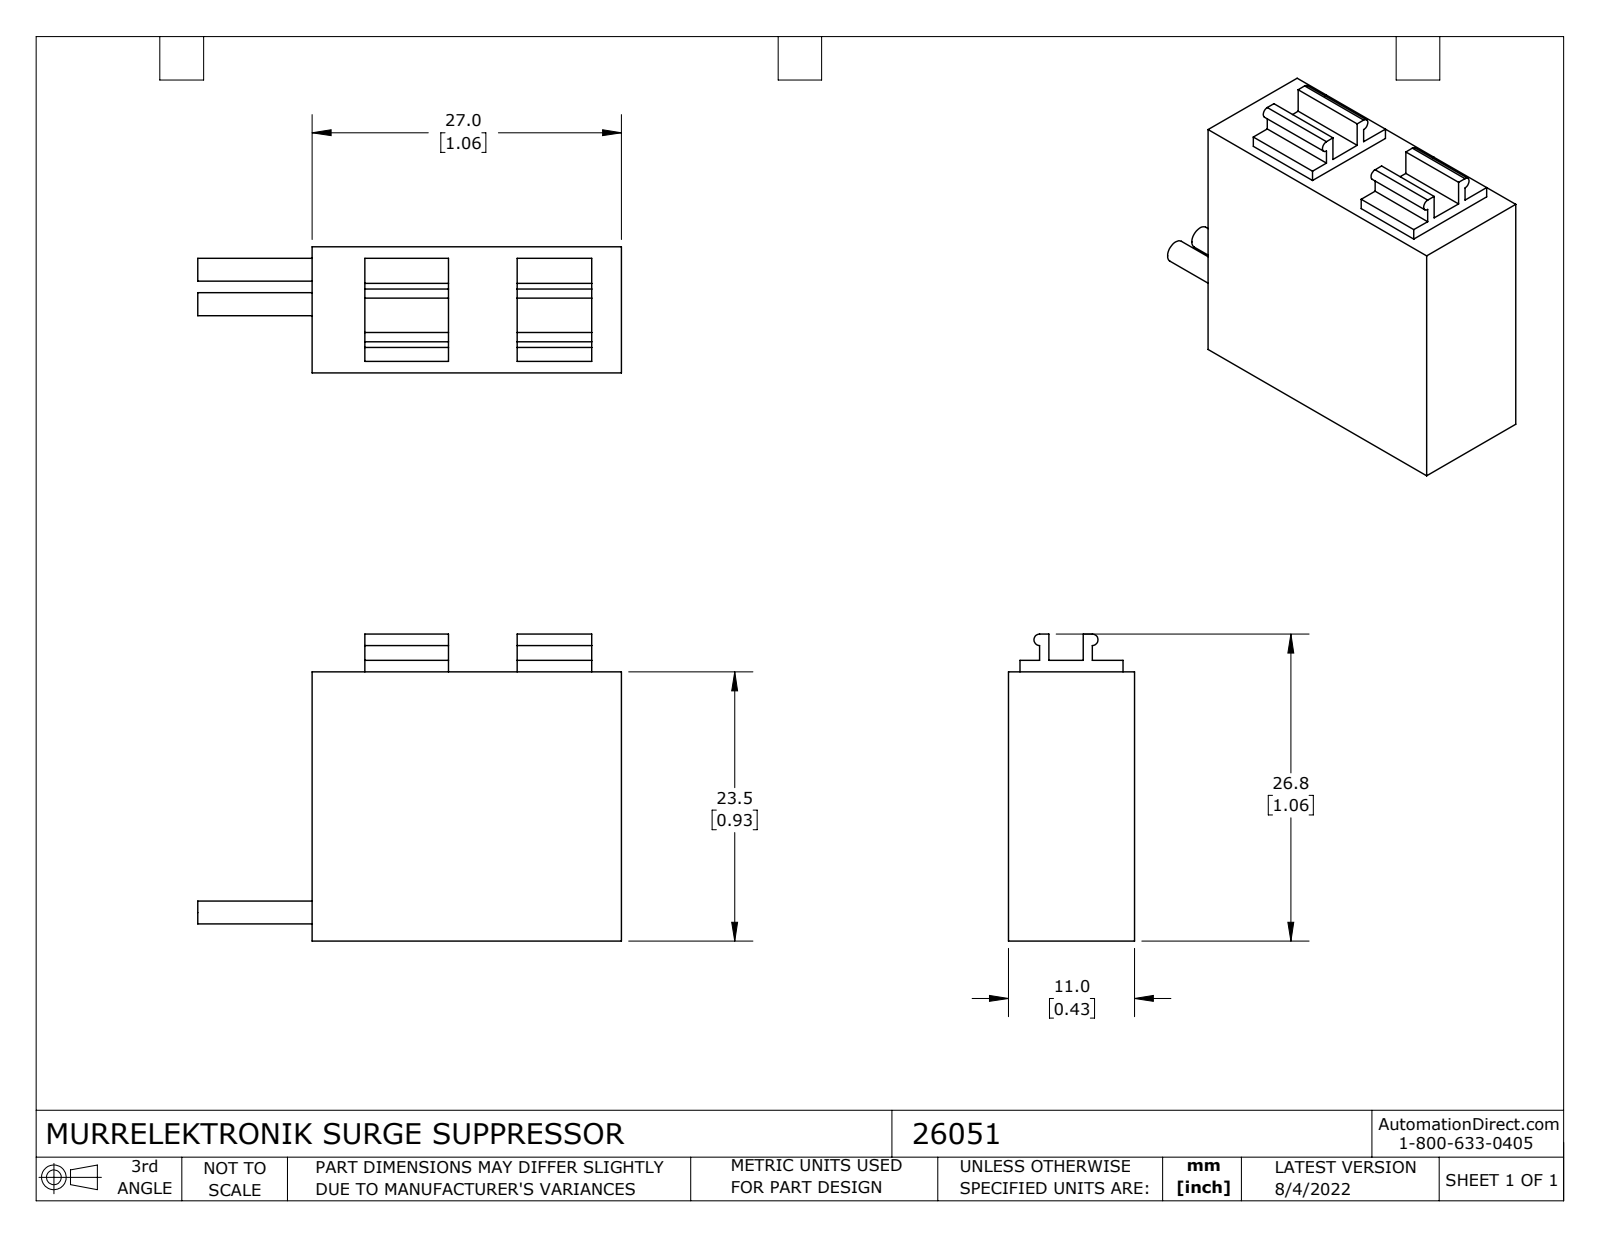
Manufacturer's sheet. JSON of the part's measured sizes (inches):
{"part_name": "26051", "step_written_by": "SolidWorks 2021 (CONFIG_CONTROL_DESIGN)", "units": "inches", "bodies": {"solids": 1, "faces": 43, "planar": 34, "cylindrical": 9, "other": 0}, "overall_size": [1.457, 1.055, 0.433], "volume_in3": 0.441, "surface_area_in2": 4.232, "round_bosses_or_shafts": [[0.079, 2]], "partial_cylinders_radius": [[0.02, 2]], "face_to_face_distances": [0.433, 1.063, 0.925, 0.039, 0.965, 0.031, 0.15, 0.394, 0.176, 0.294]}
